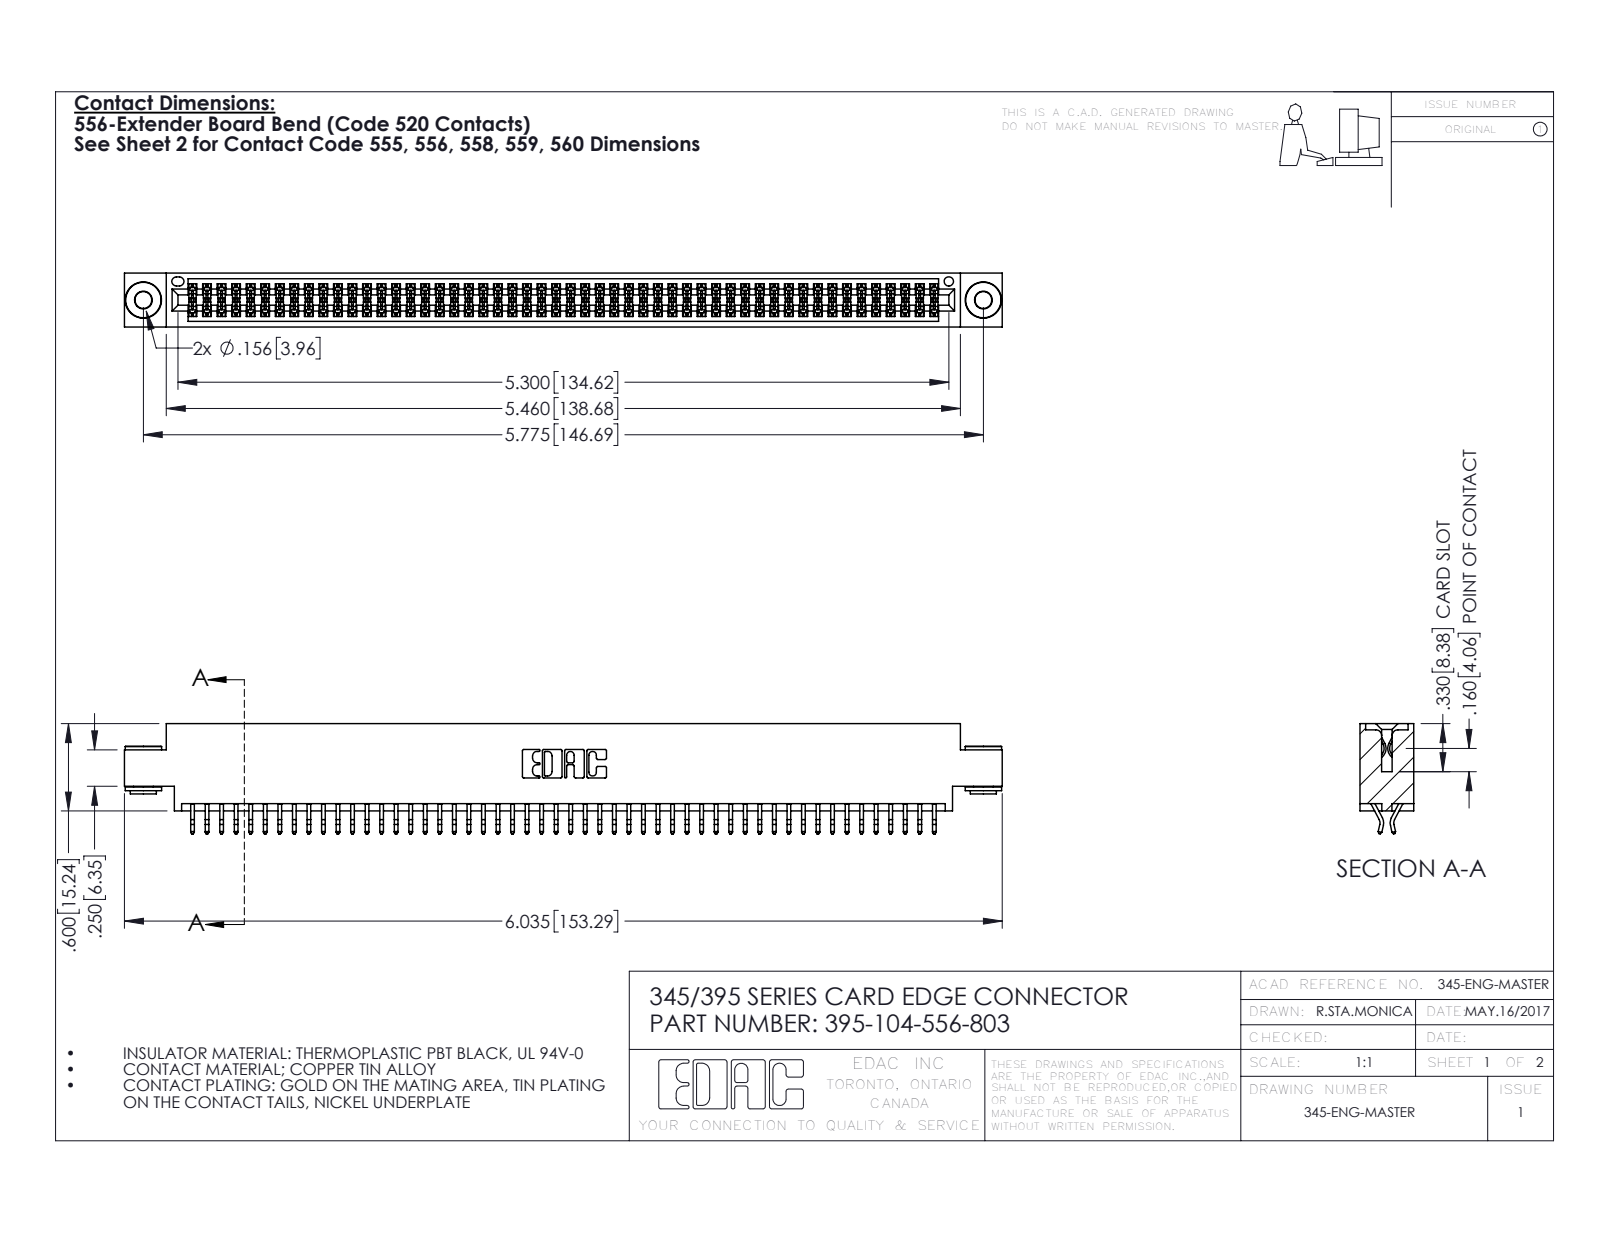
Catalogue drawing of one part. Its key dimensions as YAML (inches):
part_name: "345-250-002_345-250-002-102; 395-104-556-803; 345-292-001_556 Tail; 345 Part_0.170 Offset - 0.156 Dia-TH"
step_written_by: "SolidWorks 2016 (CONFIG_CONTROL_DESIGN)"
units: inches
bodies: {solids: 107, faces: 5992, planar: 3942, cylindrical: 2042, other: 8}
overall_size: [6.035, 0.757, 0.37]
volume: 0.908
surface_area: 34.8
round_holes:
  - {diameter: 0.116, count: 2}
  - {diameter: 0.156, count: 2}
  - {diameter: 0.064, count: 1}
round_bosses_or_shafts:
  - {diameter: 0.25, count: 2}
  - {diameter: 0.18, count: 2}
  - {diameter: 0.136, count: 2}
partial_cylinders:
  - {radius: 0.006, count: 156}
  - {radius: 0.01, count: 22}
  - {radius: 0.007, count: 6}
  - {radius: 0.031, count: 6}
  - {radius: 0.026, count: 3}
  - {radius: 0.01, count: 2}
  - {radius: 0.014, count: 2}
  - {radius: 0.019, count: 2}
face_to_face_distances: [0.072, 0.298, 0.37, 0.2, 0.025, 0.098, 0.272, 0.225, 0.175, 0.149]
hole_center_spacings: [0.27, 5.539, 5.775]
